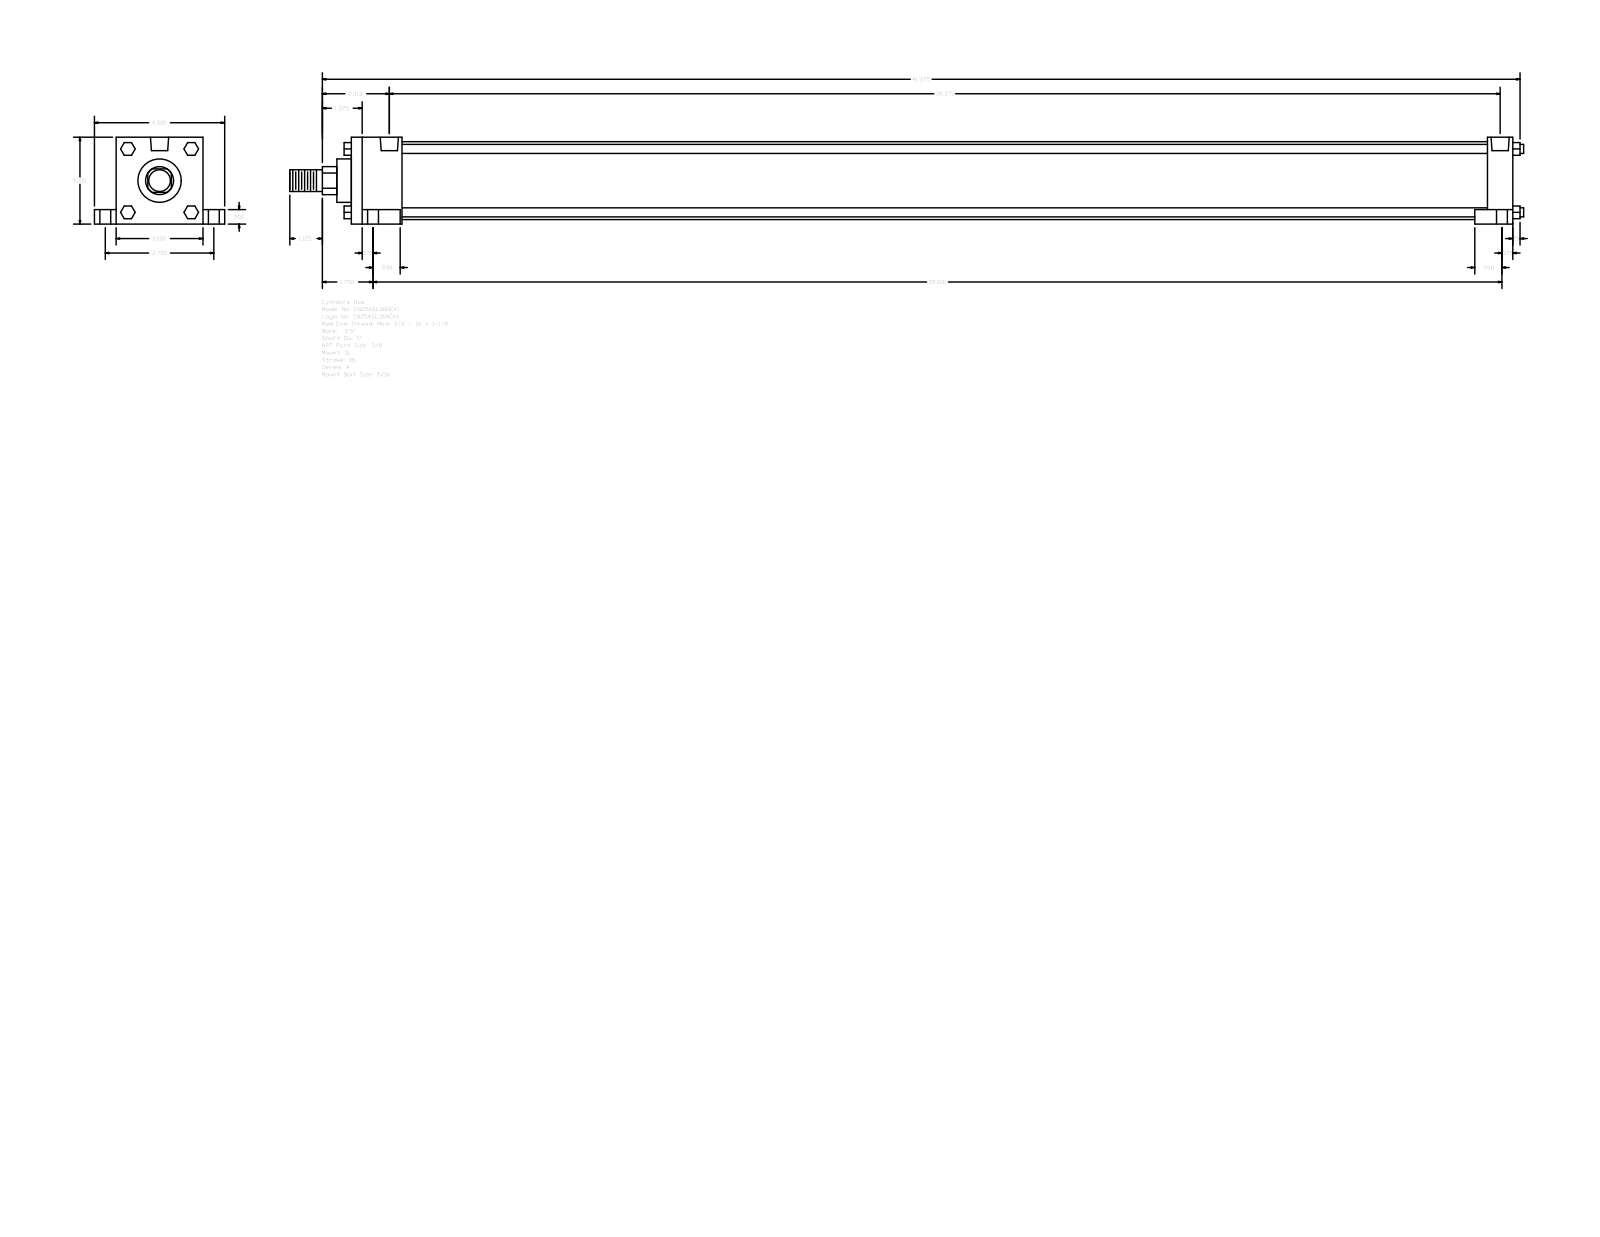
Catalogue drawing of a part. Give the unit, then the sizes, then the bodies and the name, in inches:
Units: inches
Overall size (bounding box): 42.625 × 4.5 × 3
Round holes (diameter × count): ⌀0.219 ×4, ⌀0.375 ×4, ⌀0.625 ×4, ⌀0.627 ×2
Round bosses / shafts (diameter × count): ⌀0.313 ×4, ⌀2.69 ×1, ⌀1.5 ×1, ⌀1 ×1, ⌀0.75 ×1
Partial cylindrical surfaces — rounded edges, fillets, slot ends (radius × count): R0.484 ×1
Main face-to-face distances: 3, 40.125, 0.5, 1.75, 38.375, 39.25, 37.5, 0.875, 0.75, 2.5
Hole centre spacings: 0.094, 1.875, 1.876, 1.933, 1.957, 3.75, 38.469, 38.483
Bodies: 0 solids, 148 faces (112 planar, 36 cylindrical, 0 other)
Part name (STEP PRODUCT): A_SL__0250_1
STEP written by: GSSL Pune (CONFIG_CONTROL_DESIGN)
